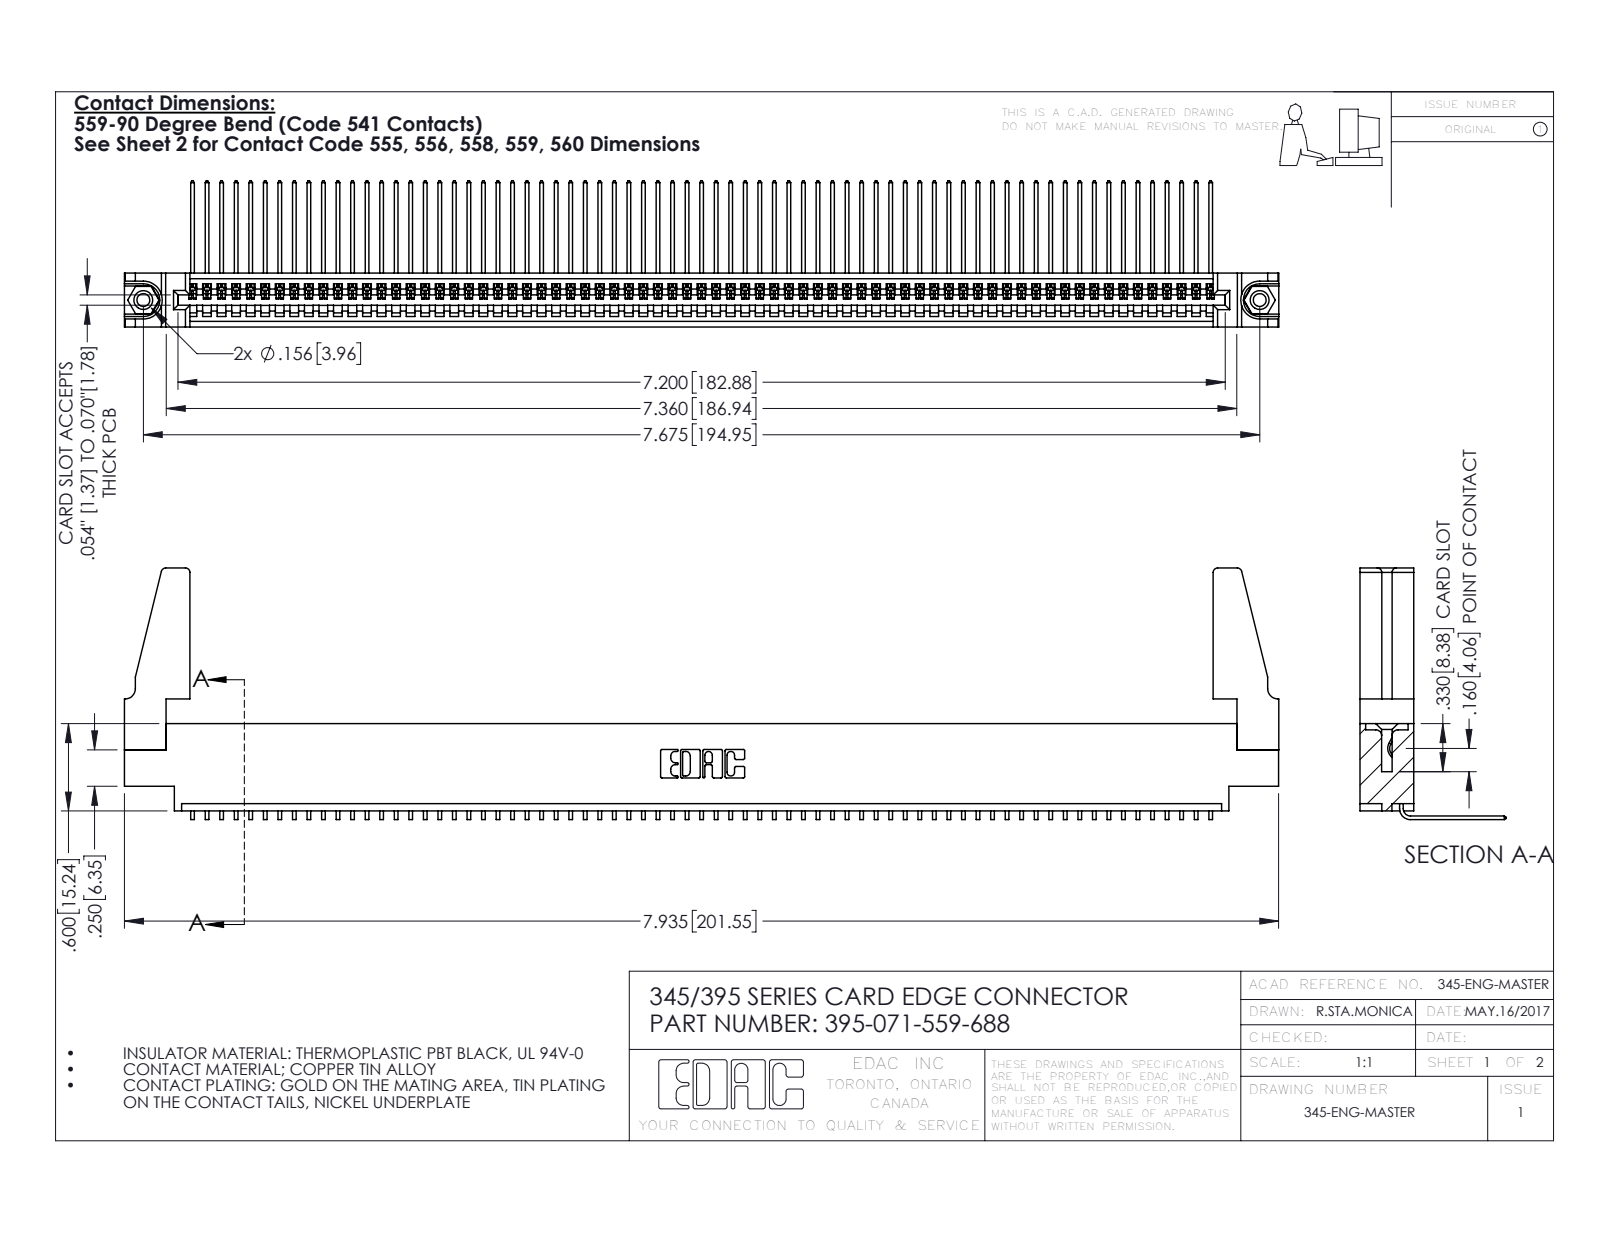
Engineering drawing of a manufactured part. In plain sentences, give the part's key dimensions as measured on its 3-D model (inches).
The part is named "345-220-078_345-220-088; 345-292-001_558 559 Tail - 1; 345 Part_0.170 Offset - 0.156 Dia-TH; 345-250-001_345-250-001-102 (+1 more)". Its 3-D file was written by "SolidWorks 2016 (CONFIG_CONTROL_DESIGN)". It is 76 solids with 4514 faces: 3138 planar, 1360 cylindrical and 16 other. Overall it measures 7.936 by 1.729 by 1.005 inches. Its volume is 1.389 cubic inches and its surface area 47.99 square inches. Round holes: 2 of diameter 0.089, 2 of diameter 0.125, 2 of diameter 0.156, 1 of diameter 0.064. Round bosses or shafts: 2 of diameter 0.155. Partial cylindrical surfaces (rounded edges, fillets, slot ends): 142 of radius 0.006, 22 of radius 0.01, 8 of radius 0.03, 6 of radius 0.007, 6 of radius 0.031, 3 of radius 0.026, 2 of radius 0.031, 2 of radius 0.04. The main face-to-face distances are 0.072, 0.298, 0.37, 0.098, 0.272, 0.025, 0.2, 0.225, 0.175, 0.149. The hole center spacings are 0.27, 7.439, 7.675.
